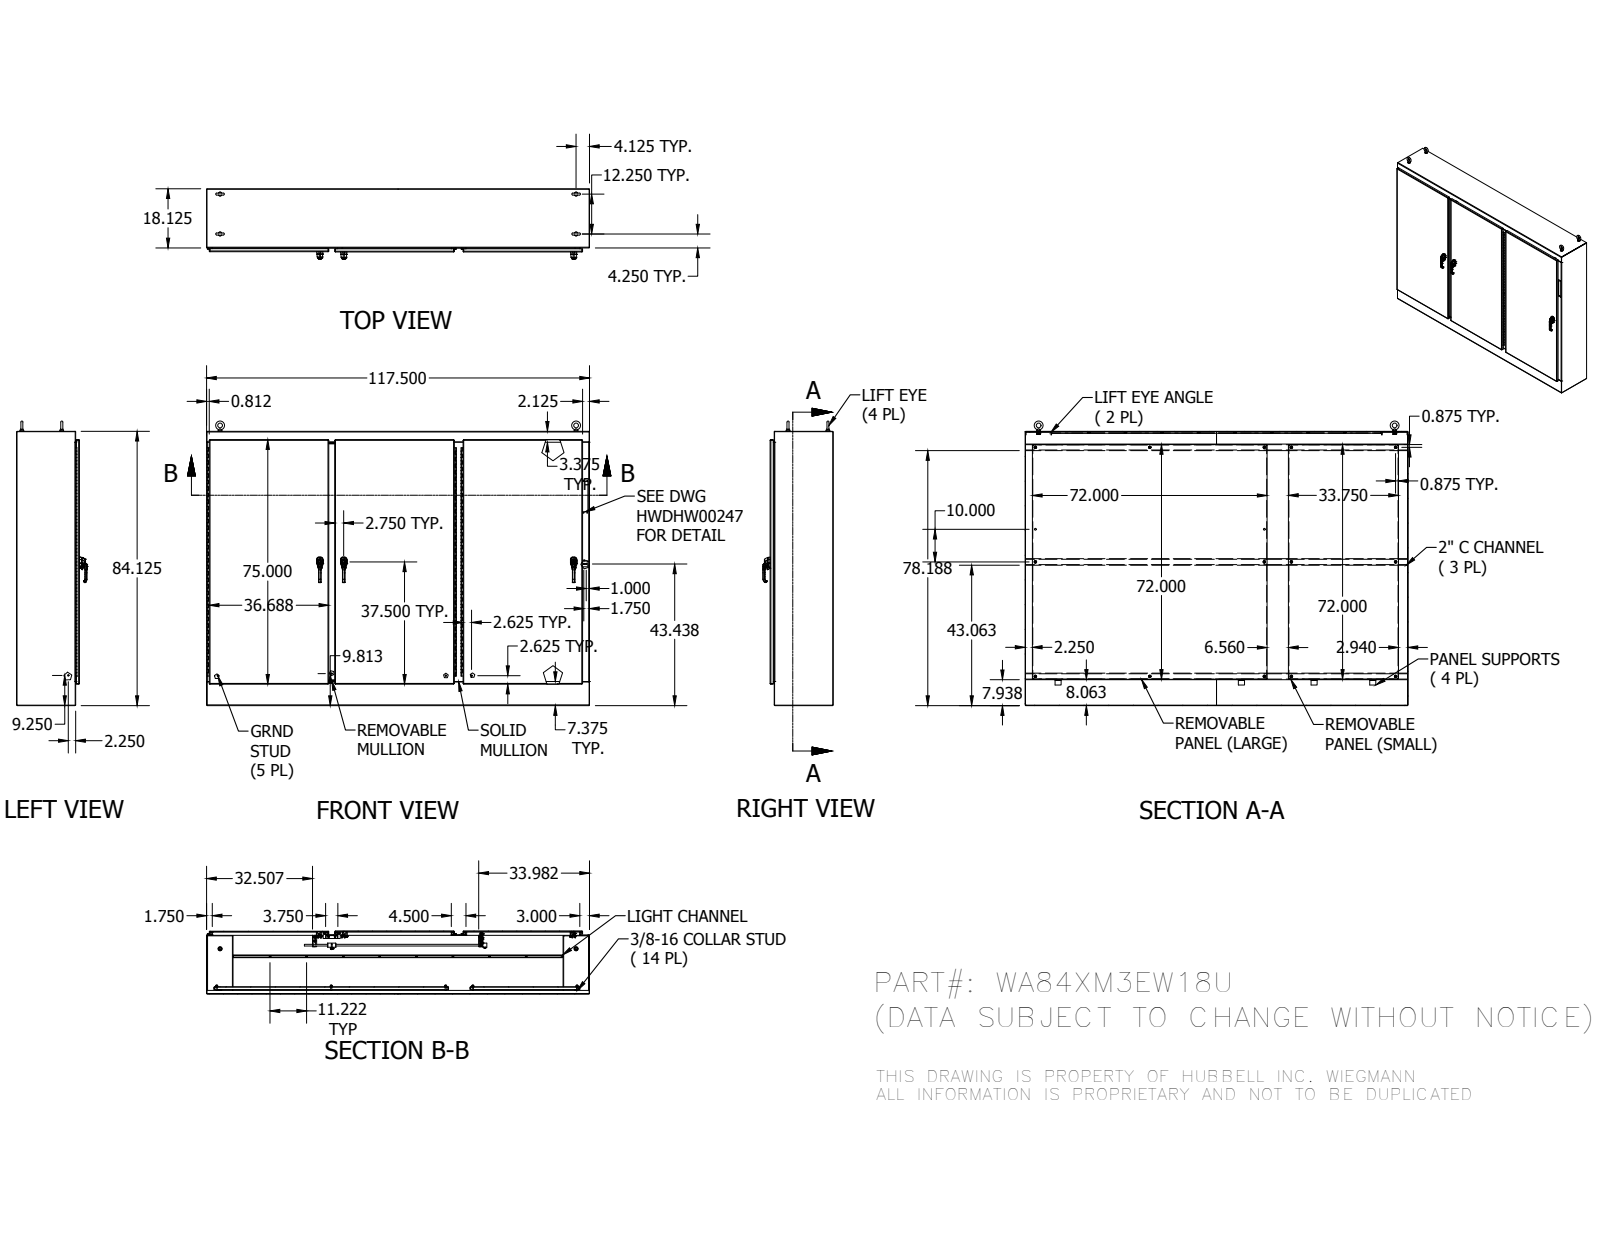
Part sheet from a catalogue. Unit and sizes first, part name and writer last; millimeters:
Units: millimetres
Overall size (bounding box): 2984.5 × 2216.09 × 548.73
Round holes (diameter × count): ⌀6.35 ×28, ⌀9.52 ×26, ⌀7.02 ×20, ⌀14.29 ×16, ⌀7.8 ×14, ⌀5.08 ×12, ⌀4.83 ×10, ⌀7.14 ×10, ⌀7.33 ×10, ⌀8.51 ×10, ⌀9.65 ×10, ⌀5.4 ×9
Round bosses / shafts (diameter × count): ⌀8.38 ×27, ⌀6.35 ×25, ⌀15.88 ×21, ⌀9.52 ×17, ⌀8.56 ×15, ⌀14.29 ×13, ⌀25.4 ×10, ⌀12.7 ×10
Partial cylindrical surfaces — rounded edges, fillets, slot ends (radius × count): R0.5 ×524, R0.3 ×322, R0.51 ×240, R0.47 ×63, R1.27 ×52, R1.59 ×48, R2 ×41, R1 ×33
Main face-to-face distances: 3.17, 488.43, 3.18, 50.8, 53.97, 57.15, 53.98, 1.59, 485.26, 434.46
Hole centre spacings: 1.6, 1784.35, 1695.13, 285.04, 1.59, 570.08, 892.17, 892.18
Volume: 83 300 000 mm³ · Surface area: 52 530 000 mm²
Bodies: 335 solids, 12779 faces (5910 planar, 4108 cylindrical, 2761 other)
Part name (STEP PRODUCT): WAXM3EW18U_TOP; HFW3025; 316298; 349132 (+8 more)
STEP written by: Autodesk Inventor 2014 (AUTOMOTIVE_DESIGN)
